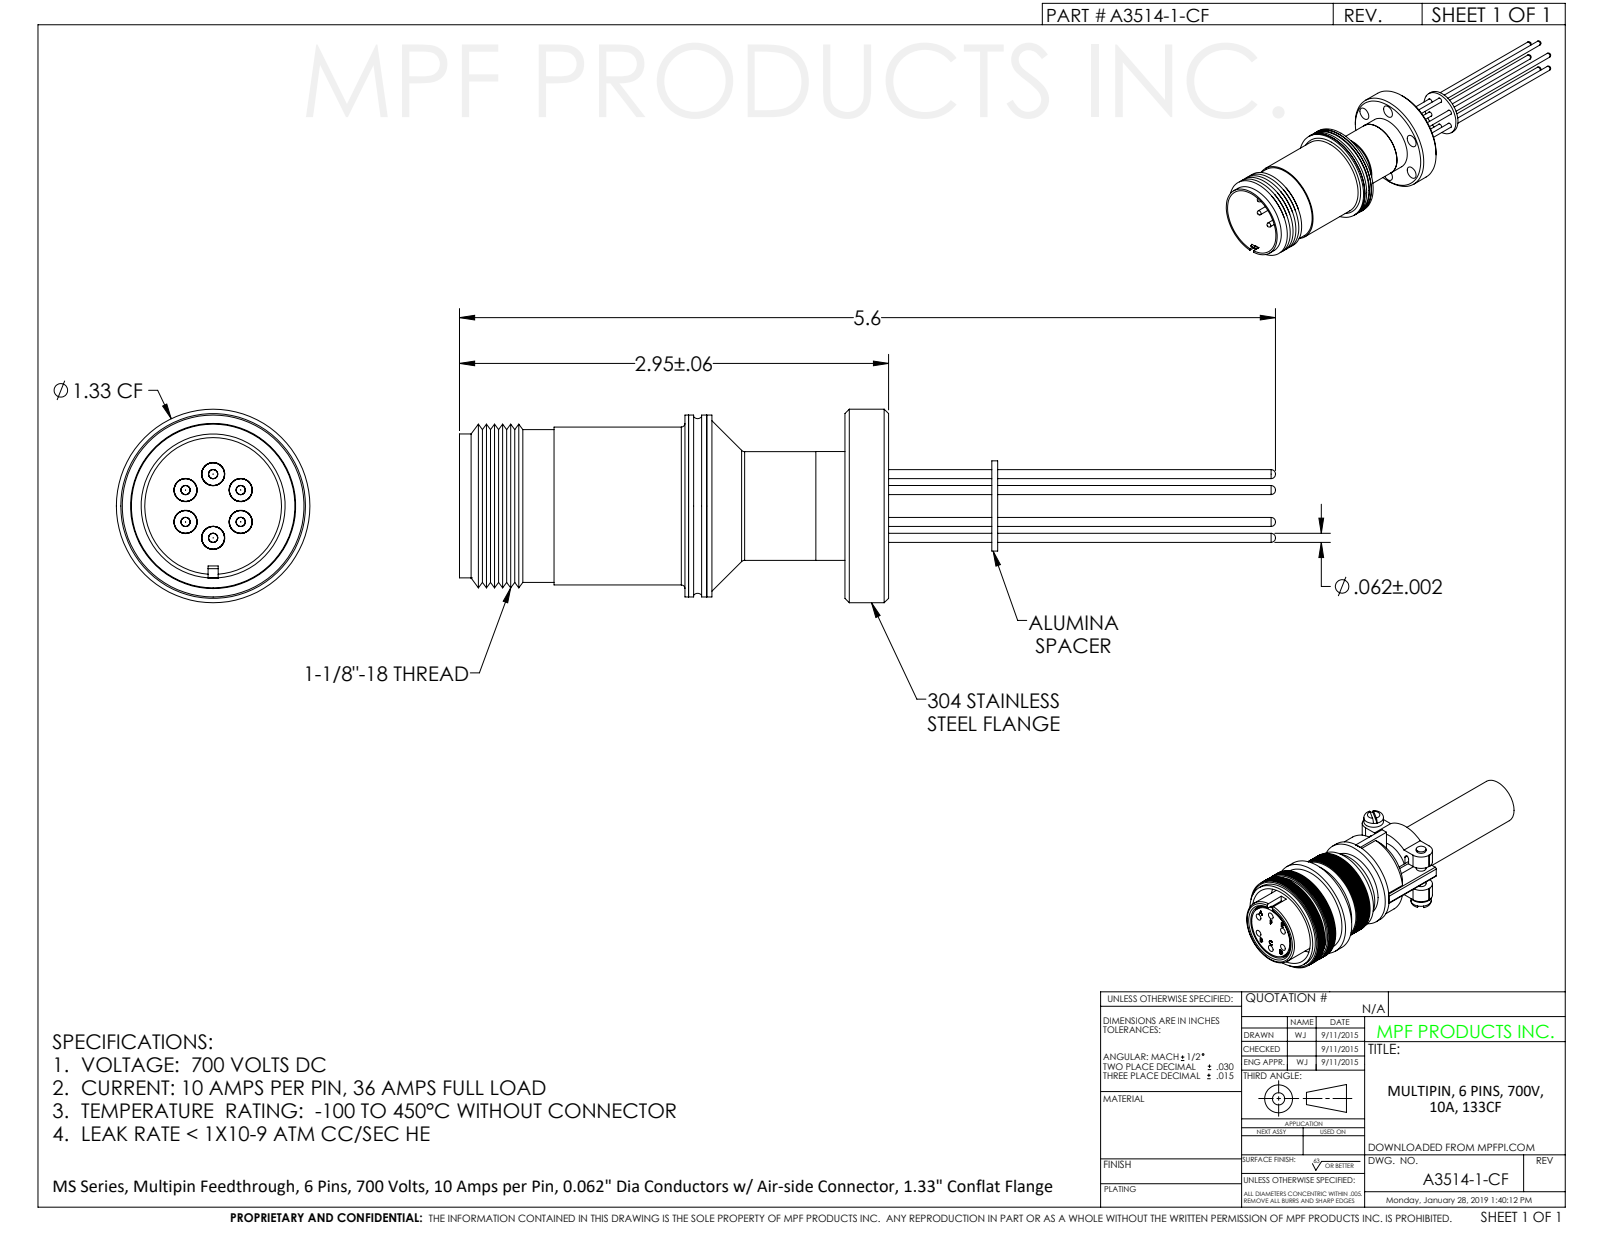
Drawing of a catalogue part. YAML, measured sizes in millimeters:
part_name: "A3514-1-CF"
step_written_by: "SolidWorks 2012 (CONFIG_CONTROL_DESIGN)"
units: millimeters
bodies: {solids: 25, faces: 373, planar: 90, cylindrical: 178, other: 105}
overall_size: [143.4, 33.8, 33.8]
volume: 16800
surface_area: 28080
round_holes:
  - {diameter: 1.5, count: 6}
  - {diameter: 1.5, count: 6}
  - {diameter: 1.6, count: 6}
  - {diameter: 3.6, count: 6}
  - {diameter: 4, count: 6}
  - {diameter: 4, count: 6}
  - {diameter: 4.4, count: 6}
  - {diameter: 16, count: 1}
  - {diameter: 17.1, count: 1}
  - {diameter: 18.4, count: 1}
  - {diameter: 21.5, count: 1}
  - {diameter: 23.9, count: 1}
round_bosses_or_shafts:
  - {diameter: 4.7, count: 6}
  - {diameter: 4, count: 6}
  - {diameter: 1.6, count: 6}
  - {diameter: 33.8, count: 1}
  - {diameter: 31.8, count: 1}
  - {diameter: 27.6, count: 1}
  - {diameter: 26.7, count: 1}
  - {diameter: 25.9, count: 1}
face_to_face_distances: [3.2, 14.1, 10.9, 34.9, 7.2, 31.8, 24.5, 27.7, 38.6, 37.3]
hole_center_spacings: [5.6, 13.5, 11.7, 17, 19.1, 23.4, 7.9, 9.6]
